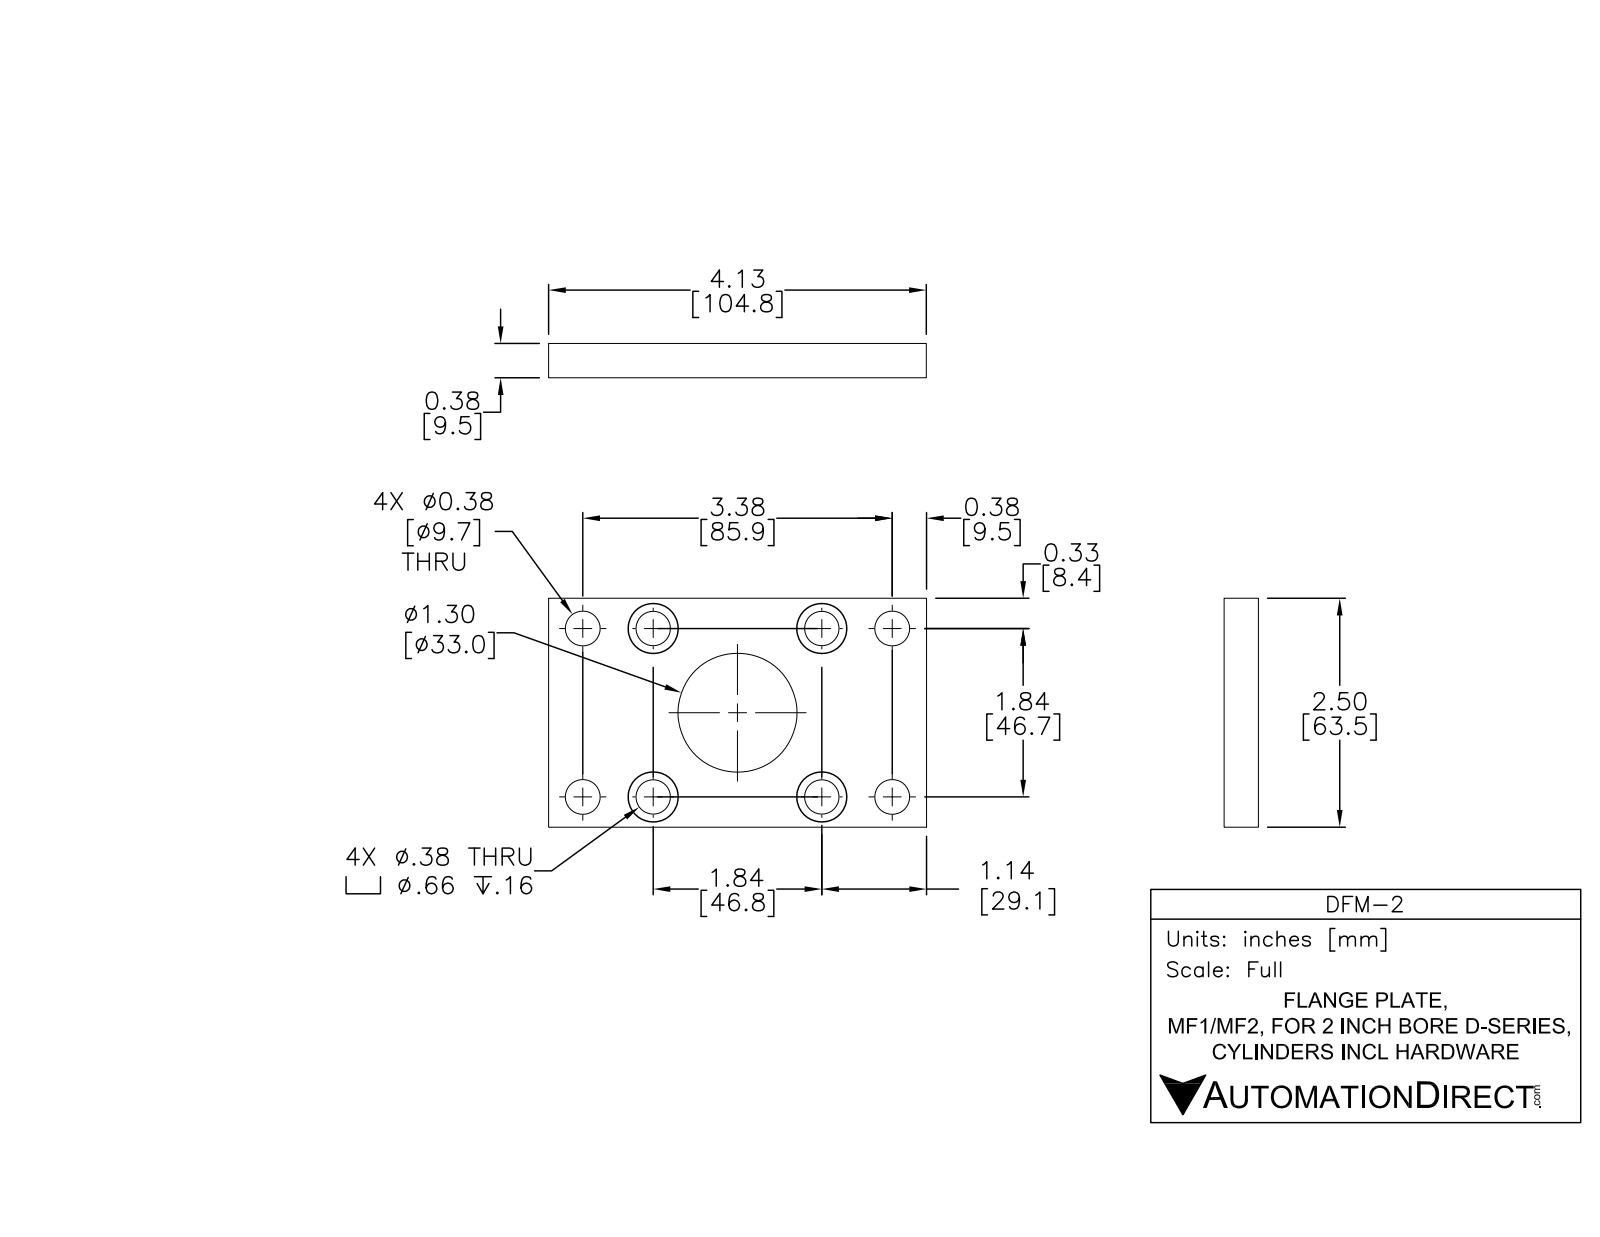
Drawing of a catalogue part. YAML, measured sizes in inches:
part_name: "DFM-2"
step_written_by: "SolidWorks 2015 (AUTOMOTIVE_DESIGN)"
units: inches
bodies: {solids: 1, faces: 40, planar: 10, cylindrical: 30, other: 0}
overall_size: [4.125, 2.5, 0.375]
volume: 2.885
surface_area: 26.62
round_holes:
  - {diameter: 0.375, count: 4}
  - {diameter: 0.375, count: 4}
  - {diameter: 0.675, count: 3}
  - {diameter: 0.675, count: 1}
  - {diameter: 1.3, count: 1}
face_to_face_distances: [0.375, 2.5, 0.155, 0.22, 4.125]
hole_center_spacings: [1.844, 0.765, 1.304, 1.923, 1.996, 2.609, 3.195, 2.608]
